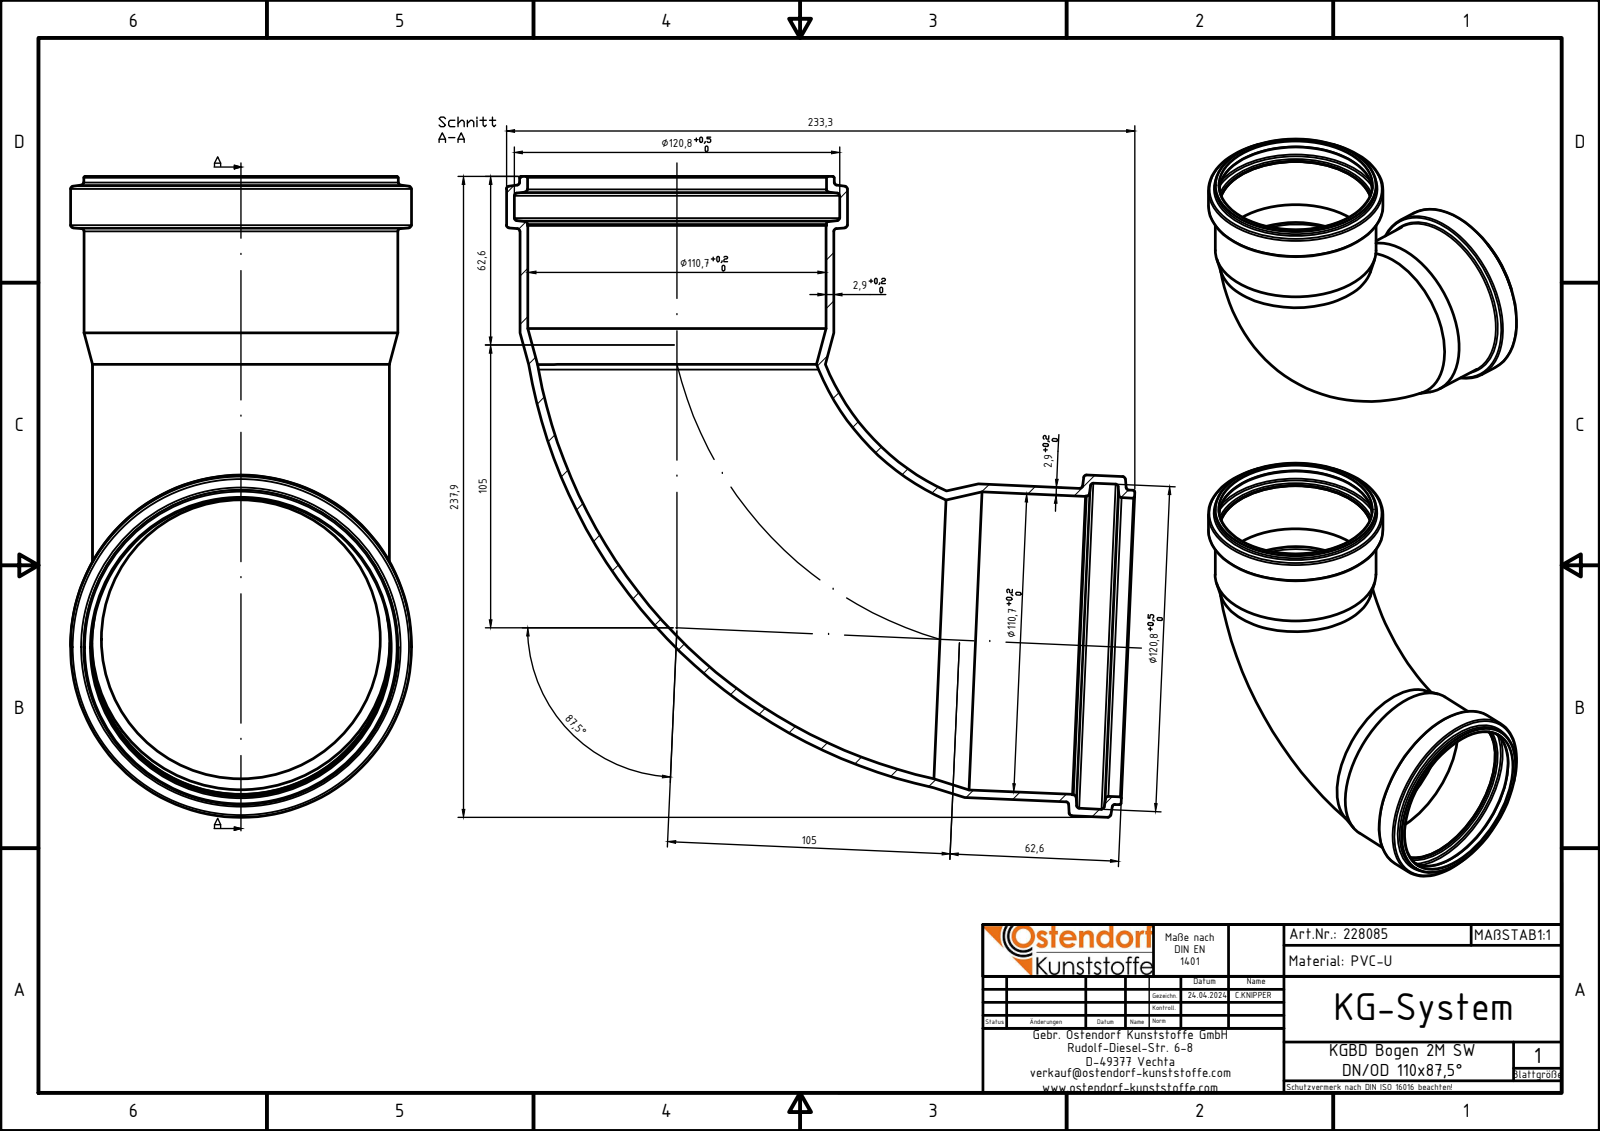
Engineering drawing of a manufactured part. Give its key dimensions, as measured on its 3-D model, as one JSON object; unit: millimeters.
{"part_name": "228085z", "step_written_by": "Autodesk Inventor 2024 (AUTOMOTIVE_DESIGN)", "units": "millimeters", "bodies": {"solids": 1, "faces": 53, "planar": 4, "cylindrical": 14, "other": 35}, "overall_size": [237.95, 233.27, 126.6], "volume_mm3": 329524, "surface_area_mm2": 213032, "round_holes": [[110.7, 2], [111, 2], [120.8, 2]], "round_bosses_or_shafts": [[126.6, 2], [116.8, 2], [116.5, 2]], "face_to_face_distances": [18.2]}
